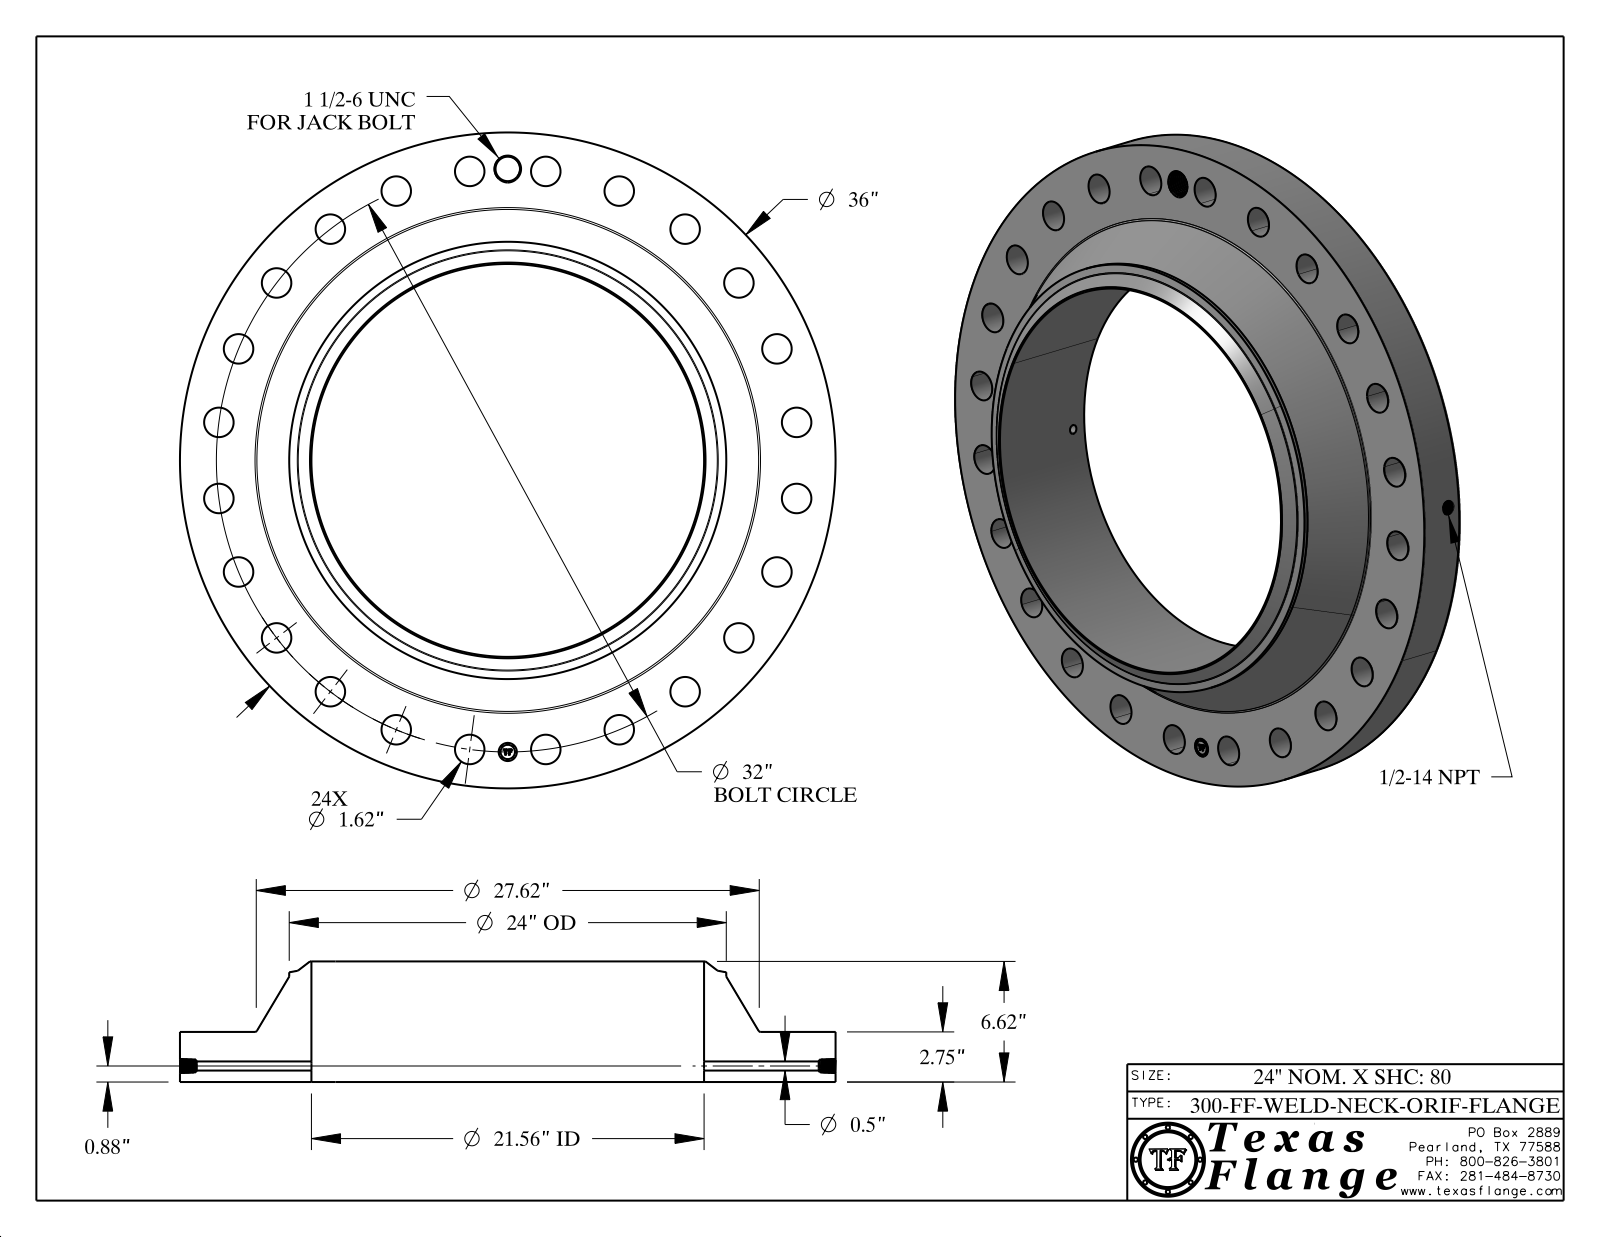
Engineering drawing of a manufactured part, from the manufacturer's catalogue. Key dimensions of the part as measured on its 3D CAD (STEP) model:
Part name (STEP PRODUCT): 300-FF-WELD-NECK
STEP written by: CATIA V5 STEP AP214 (AUTOMOTIVE_DESIGN)
Units: inches
Bodies: 1 solid, 811 faces (368 planar, 127 cylindrical, 316 other)
Overall size (bounding box): 36 × 36 × 6.62
Volume: 2 175 in³ · Surface area: 2 511 in²
Round holes (diameter × count): ⌀1.62 ×24, ⌀0.5 ×1, ⌀0.672 ×1, ⌀1 ×1, ⌀1.344 ×1, ⌀21.562 ×1
Round bosses / shafts (diameter × count): ⌀0.061 ×8, ⌀36 ×1, ⌀24 ×1, ⌀0.788 ×1
Main face-to-face distances: 2.75, 6.62, 3.87, 2.735, 0.015, 3.885, 0.298, 0.293, 0.054, 0.248
Hole centre spacings: 16, 27.713, 30.909, 4.177, 19.48, 31.726, 8.282, 12.246
